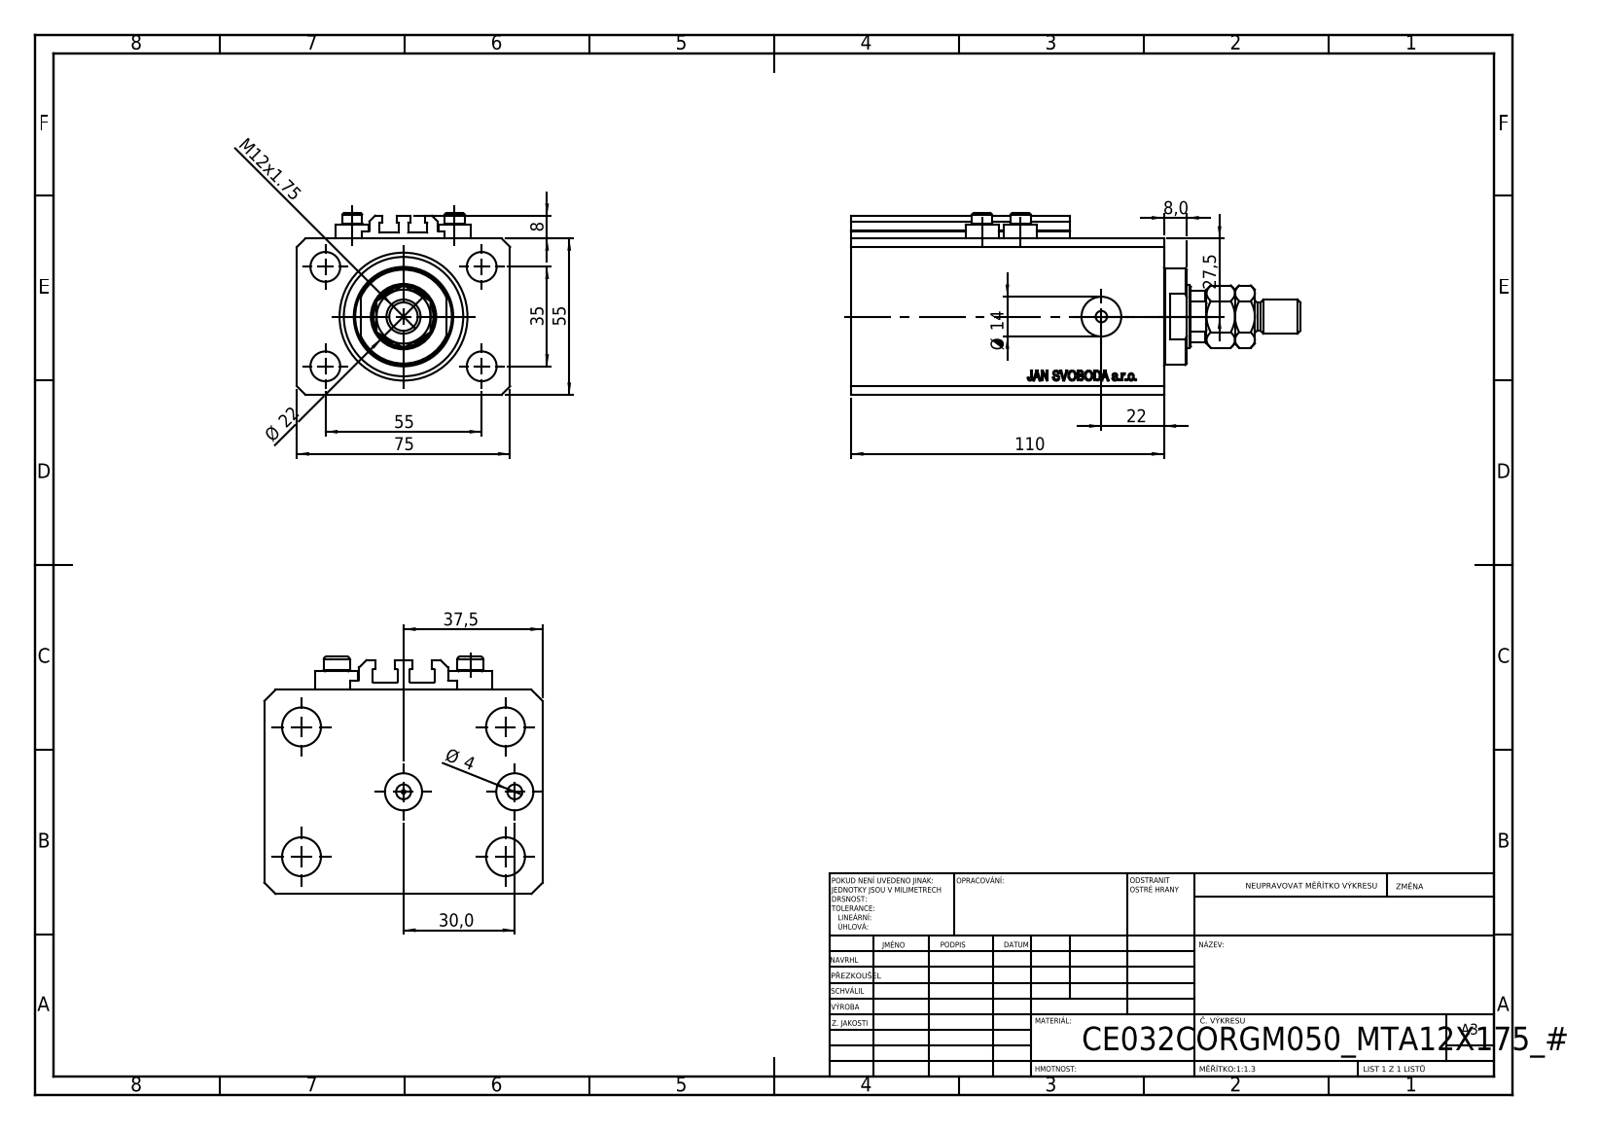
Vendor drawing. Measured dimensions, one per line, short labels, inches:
name: MTA; ALLEN BOLT V250CE; V250CE_C_Body; V250CE_VC_C (+1 more)
written by: SolidWorks 2019 (CONFIG_CONTROL_DESIGN)
unit: in
bodies: 9 solids, 1087 faces (519 planar, 92 cylindrical, 476 other)
size: 6.22 × 2.953 × 2.52
volume: 25.35 in³; area: 145.6 in²
holes: 8× ⌀0.157, 5× ⌀0.413, 2× ⌀0.394, 2× ⌀0.551, 1× ⌀0.049, 1× ⌀0.866, 1× ⌀1.26, 1× ⌀1.772
bosses: 4× ⌀0.457, 4× ⌀0.276, 1× ⌀1.339, 1× ⌀0.472
rounds: 10× R0.008, 1× R0.413
face distances: 2.165, 2.953, 4.331, 0.591, 3.74, 0.39, 3.35, 3.941, 0.098, 0.315
hole spacings: 1.283, 0.535, 0.696, 1.378, 1.417, 1.515, 2.165, 2.366
